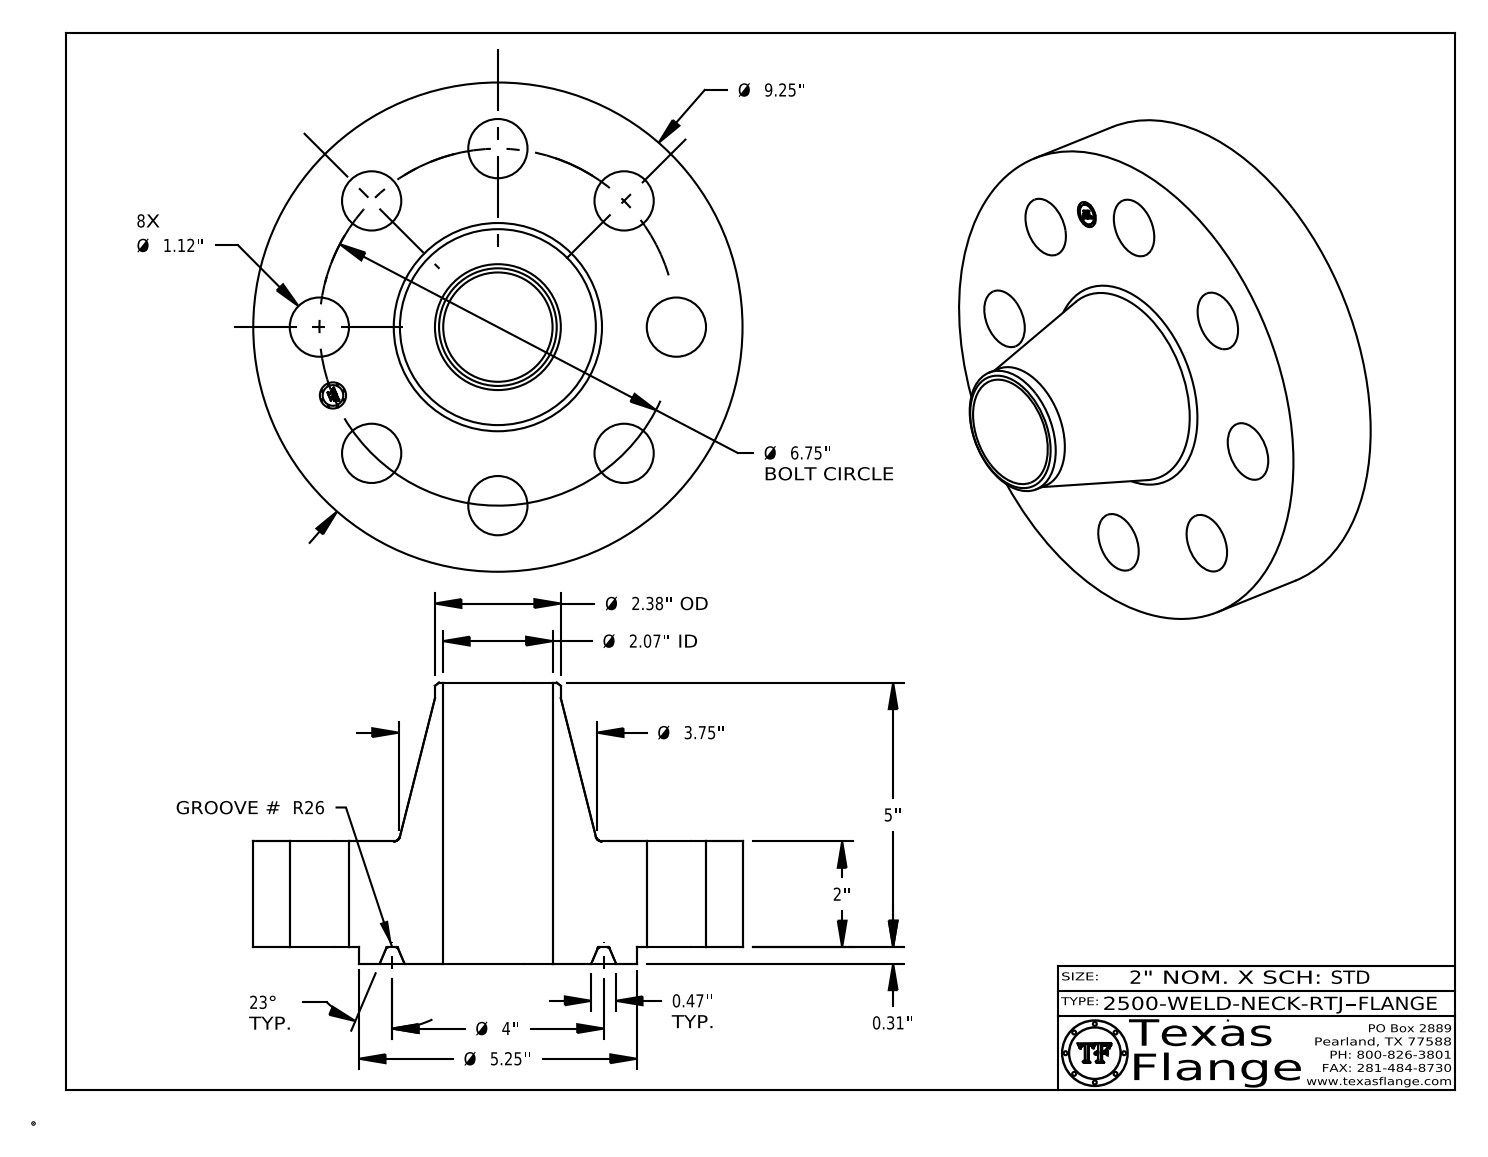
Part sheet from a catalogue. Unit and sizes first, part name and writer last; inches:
Units: inches
Overall size (bounding box): 9.25 × 9.25 × 5.313
Round holes (diameter × count): ⌀1.12 ×8, ⌀0.495 ×1, ⌀2.067 ×1
Round bosses / shafts (diameter × count): ⌀0.03 ×8, ⌀9.25 ×1, ⌀5.25 ×1, ⌀2.38 ×1, ⌀0.39 ×1
Main face-to-face distances: 2, 0.313, 2.313, 5.313, 5, 3, 2.298, 1.985, 0.015, 3.015
Hole centre spacings: 3.375, 2.583, 4.773, 6.237, 6.75, 1.317, 5.613, 6.62
Volume: 127.9 in³ · Surface area: 293 in²
Bodies: 1 solid, 429 faces (371 planar, 44 cylindrical, 14 other)
Part name (STEP PRODUCT): 2500-WELD-NECK-RTJ
STEP written by: CATIA V5 STEP AP214 (AUTOMOTIVE_DESIGN)
